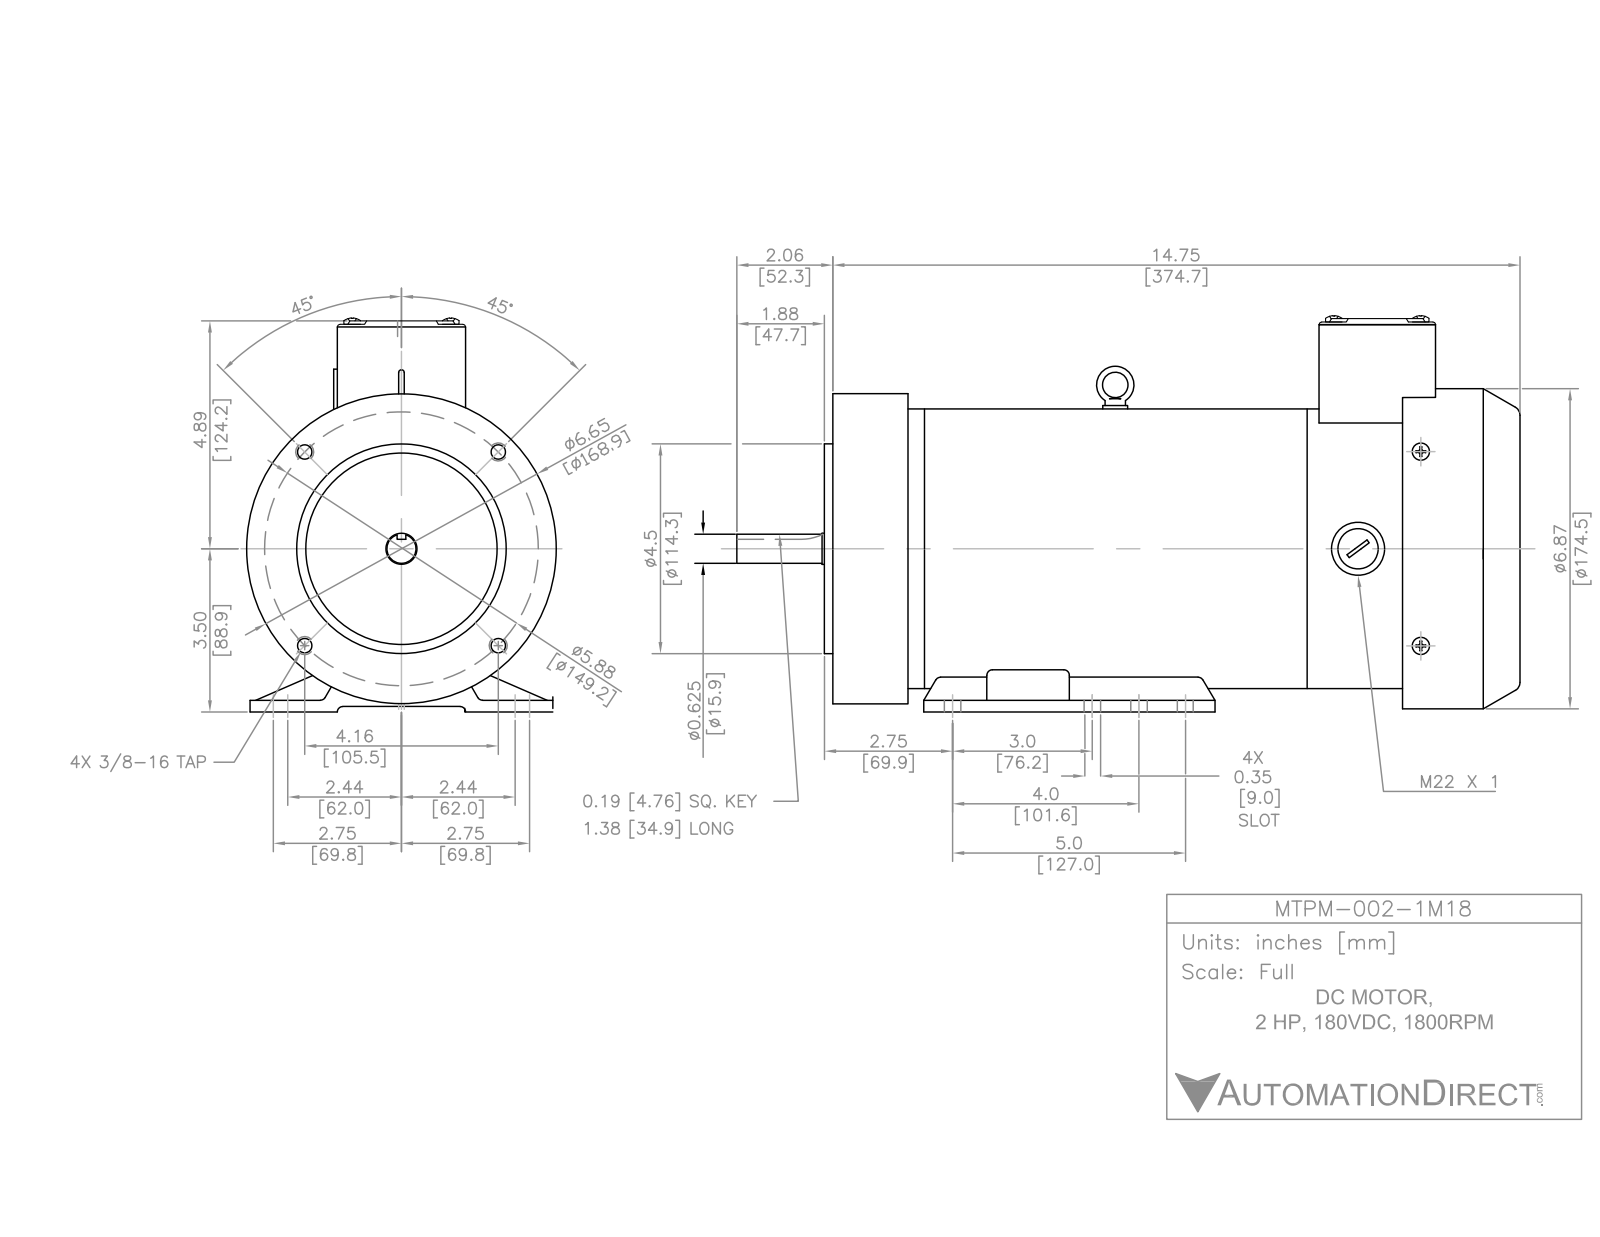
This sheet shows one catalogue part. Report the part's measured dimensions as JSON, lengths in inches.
{"part_name": "MTPM-002-1M18 Coord", "step_written_by": "SolidWorks 2024 (AUTOMOTIVE_DESIGN)", "units": "inches", "bodies": {"solids": 33, "faces": 2125, "planar": 921, "cylindrical": 795, "other": 409}, "overall_size": [16.811, 9.304, 9.304], "volume_in3": 123.8, "surface_area_in2": 1179, "round_holes": [[0.354, 7], [0.335, 6], [0.394, 5], [0.165, 4], [0.268, 3], [0.157, 2], [0.205, 2], [0.433, 2], [0.945, 2], [1.181, 2], [1.22, 2], [0.118, 1]], "round_bosses_or_shafts": [[0.354, 6], [0.331, 6], [0.157, 6], [0.39, 3], [1.181, 2], [6.866, 1], [6, 1], [4.5, 1]], "partial_cylinders_radius": [[0.02, 40], [0.197, 37], [0.079, 28], [0.394, 14], [0.039, 8], [0.059, 8], [0.098, 8], [0.177, 8]], "face_to_face_distances": [0.039, 0.118, 2.559, 0.031, 1.656, 1.687, 0.197, 4.443, 4.411, 2.756], "hole_center_spacings": [1.772, 1.772, 3.544, 2.863, 4.326, 2.102, 2.937, 3.883]}
